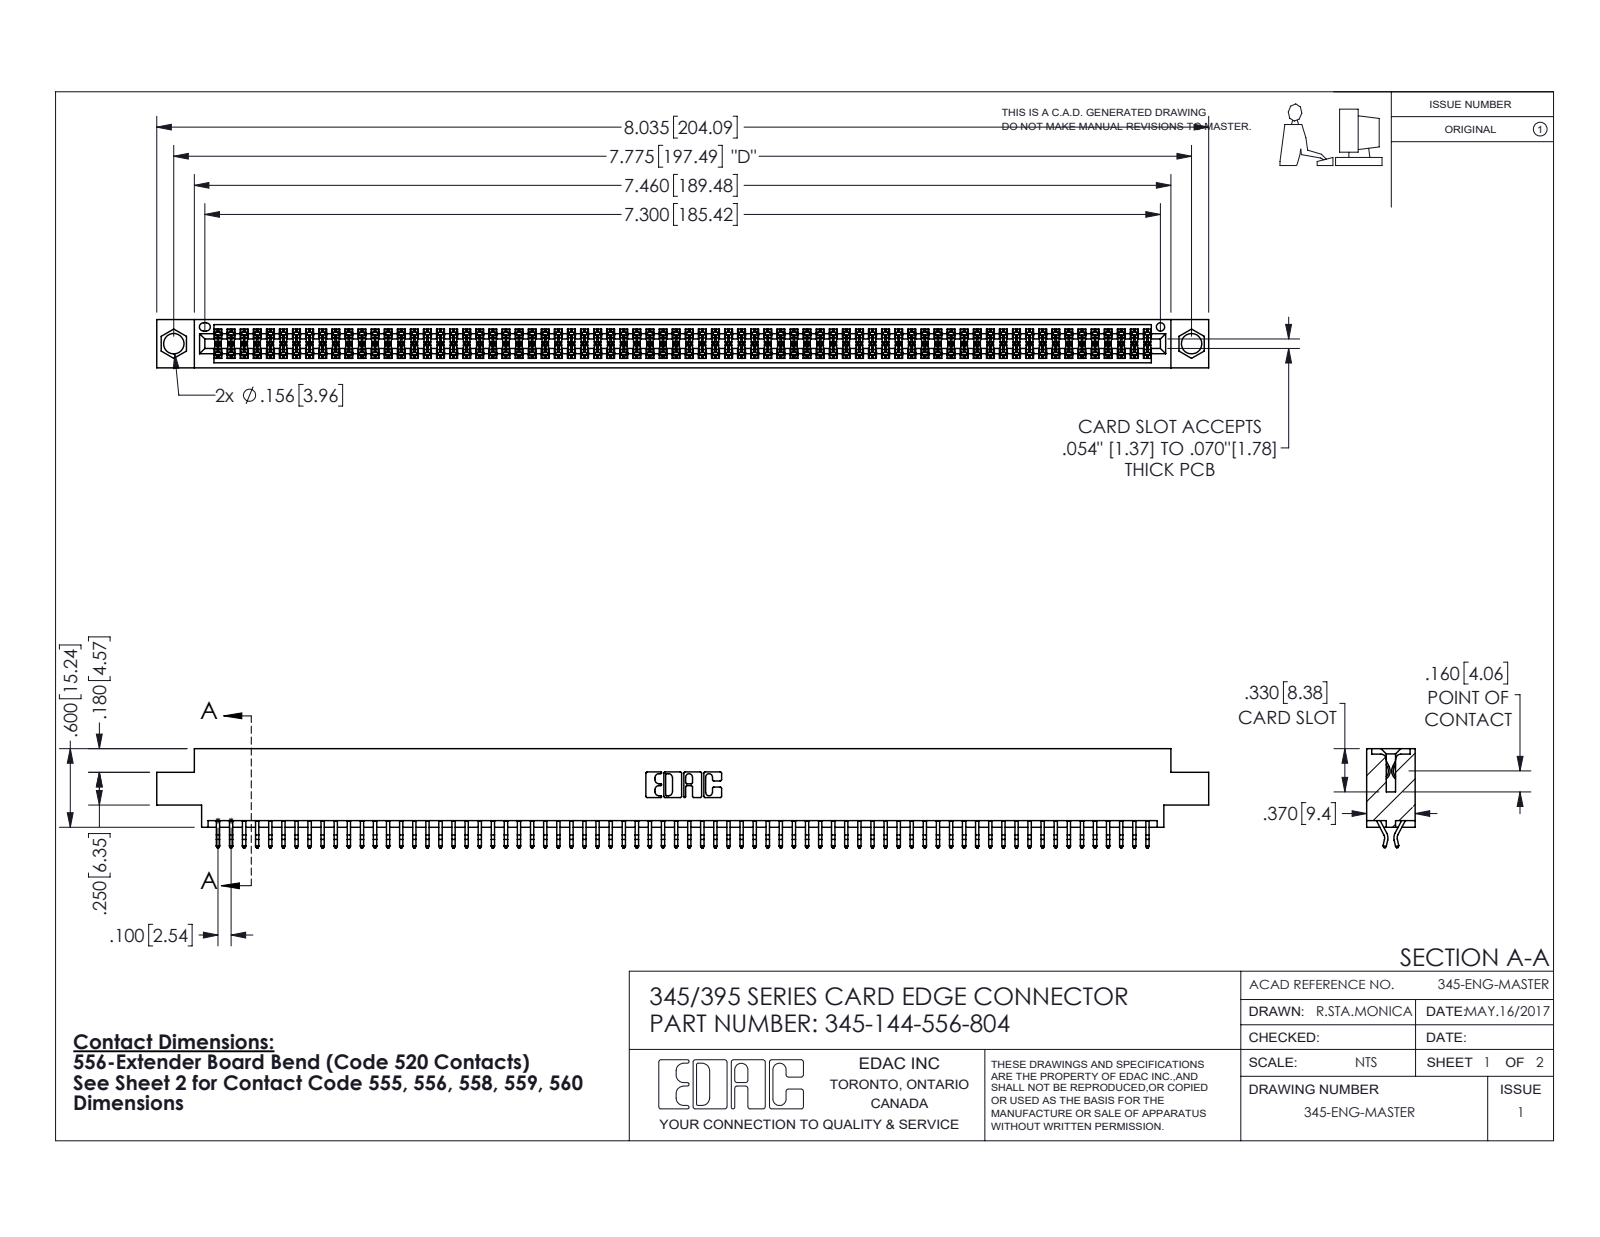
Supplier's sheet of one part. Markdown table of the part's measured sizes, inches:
| quantity | value |
| --- | --- |
| part name | 345 Part_0.170 Offset - 0.156 Dia-TI; 345-144-556-804; 345-292-001_556 Tail |
| STEP written by | SolidWorks 2020 (CONFIG_CONTROL_DESIGN) |
| units | inches |
| bodies | 145 solids, 8208 faces (5426 planar, 2782 cylindrical, 0 other) |
| overall size | 8.035 × 0.757 × 0.37 |
| volume | 1.213 in³ |
| surface area | 46.24 in² |
| round holes (diameter × count) | 0.156 × 2, 0.064 × 1 |
| partial cylindrical surfaces (radius × count) | 0.006 × 288, 0.01 × 22, 0.007 × 6, 0.031 × 6, 0.026 × 3, 0.01 × 2, 0.014 × 2, 0.019 × 2 |
| main face-to-face distances | 0.072, 0.298, 0.37, 0.2, 0.025, 0.098, 0.272, 0.225, 0.175, 0.149 |
| hole center spacings | 0.27, 7.539, 7.775 |
